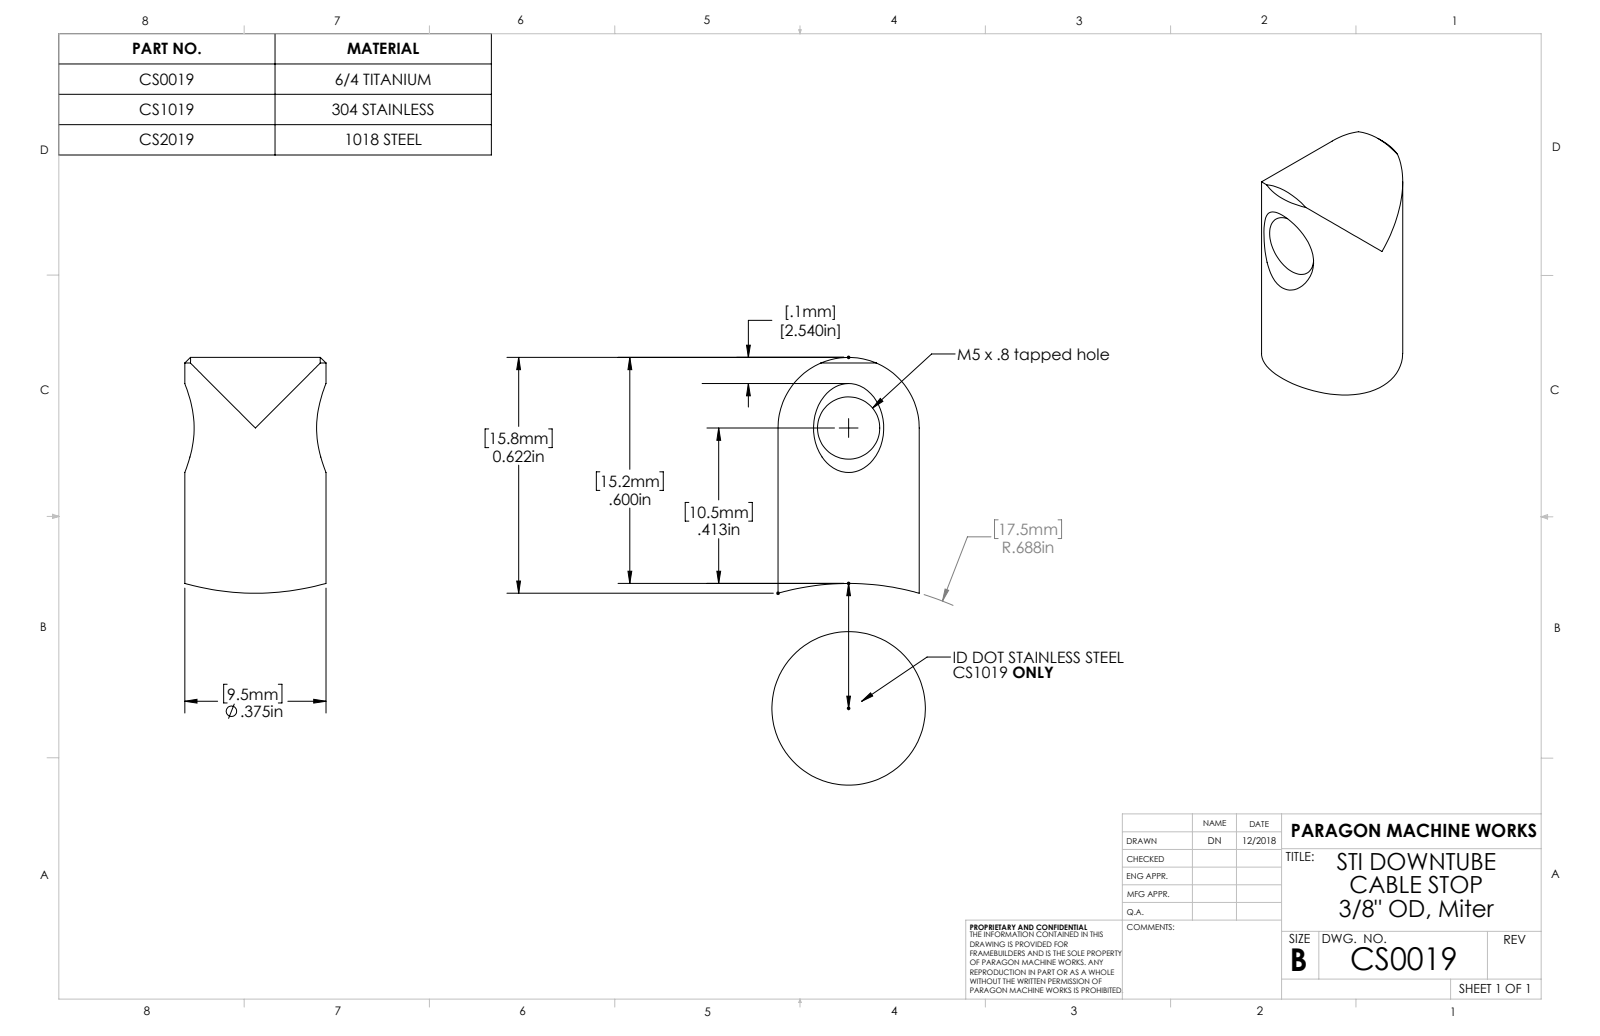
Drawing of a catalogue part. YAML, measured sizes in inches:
part_name: "CS0019"
step_written_by: "SolidWorks 2012 (AUTOMOTIVE_DESIGN)"
units: inches
bodies: {solids: 1, faces: 13, planar: 0, cylindrical: 6, other: 7}
overall_size: [0.627, 0.375, 0.375]
volume: 0.056
surface_area: 1.016
round_holes:
  - {diameter: 0.165, count: 1}
round_bosses_or_shafts:
  - {diameter: 0.375, count: 1}
partial_cylinders:
  - {radius: 0.187, count: 1}
  - {radius: 0.687, count: 1}
